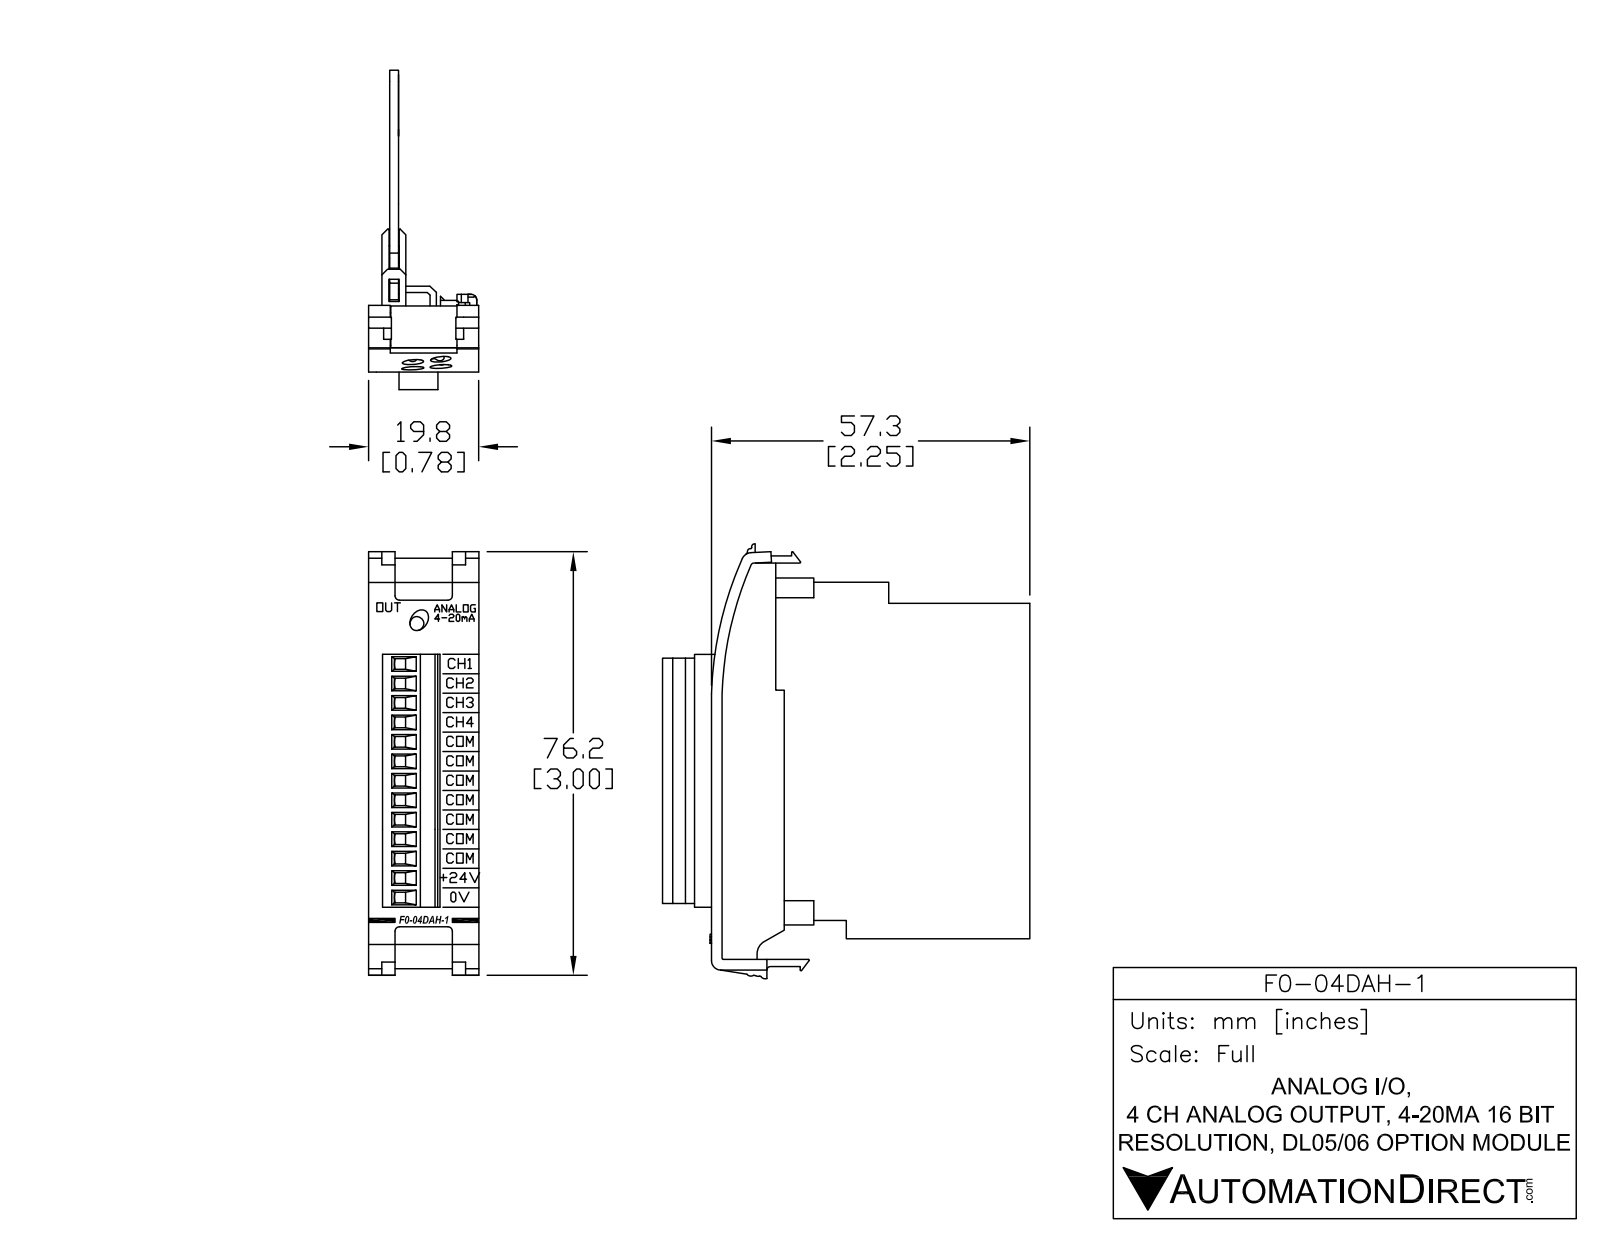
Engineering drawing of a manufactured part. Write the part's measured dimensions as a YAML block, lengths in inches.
part_name: "F0-04DAH-1"
step_written_by: "SolidWorks 2009 (AUTOMOTIVE_DESIGN)"
units: inches
bodies: {solids: 2, faces: 377, planar: 312, cylindrical: 38, other: 27}
overall_size: [3.08, 2.542, 0.826]
volume: 0.753
surface_area: 24.15
round_bosses_or_shafts:
  - {diameter: 0.08, count: 1}
partial_cylinders:
  - {radius: 0.005, count: 4}
  - {radius: 0.02, count: 3}
  - {radius: 0.035, count: 3}
  - {radius: 0.025, count: 2}
  - {radius: 0.01, count: 1}
  - {radius: 0.065, count: 1}
  - {radius: 0.07, count: 1}
  - {radius: 0.1, count: 1}
face_to_face_distances: [0.063, 0.05, 0.631, 0.075, 0.113, 0.581, 0.518, 0.681, 0.568, 0.06]
